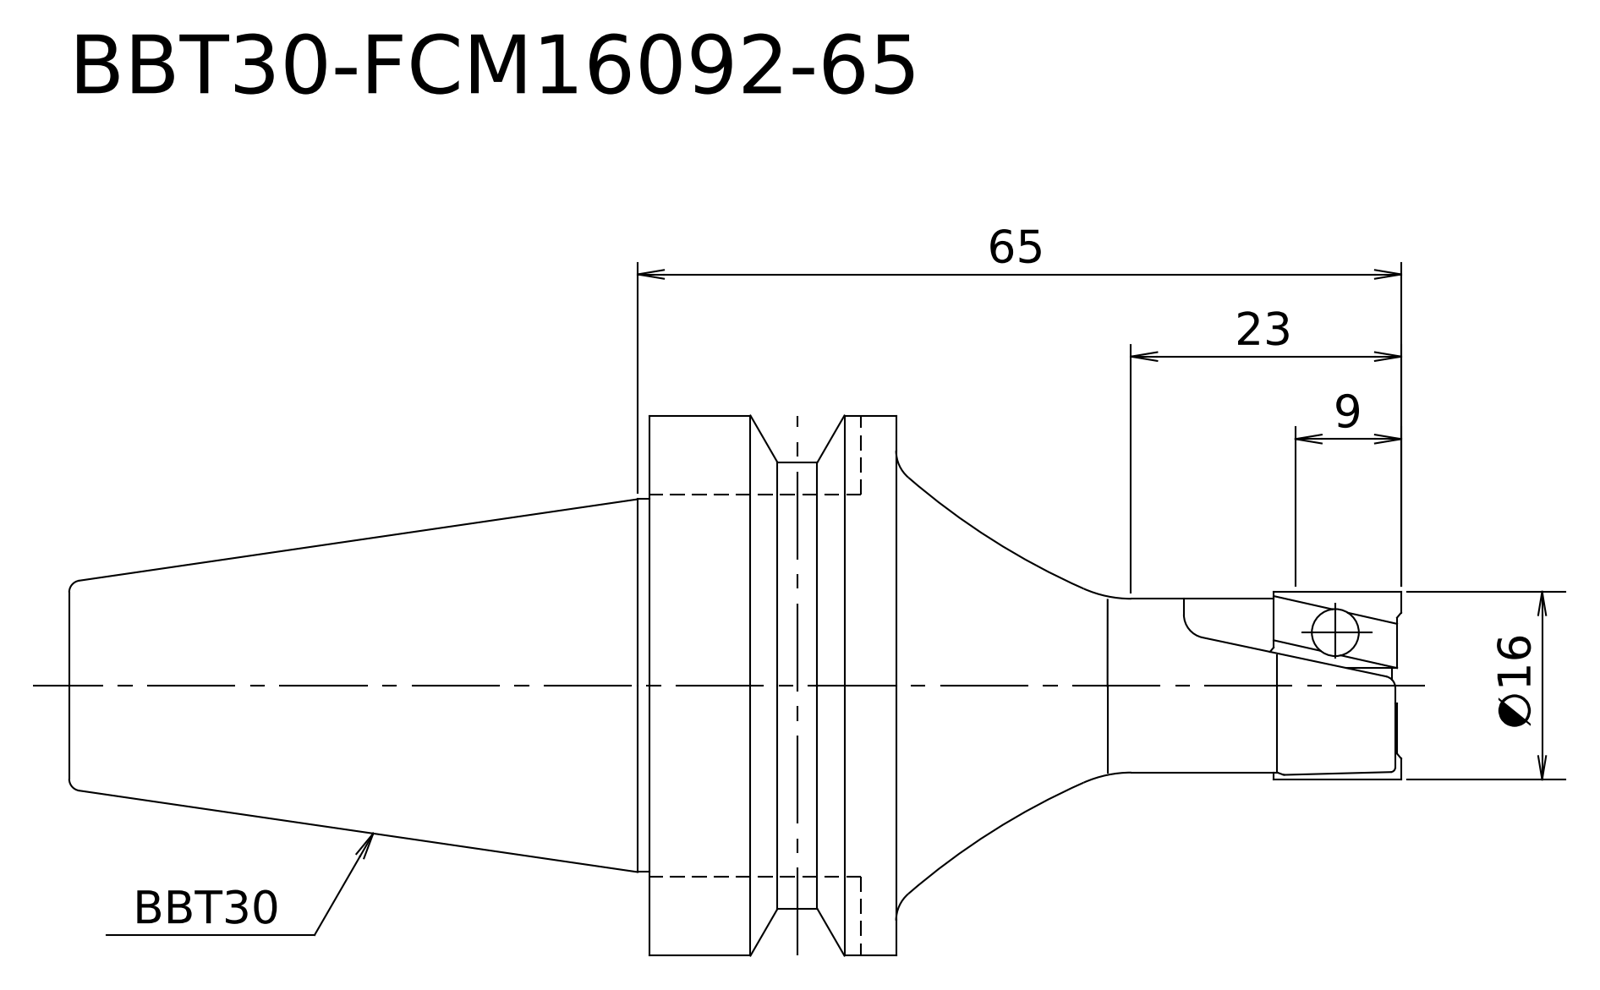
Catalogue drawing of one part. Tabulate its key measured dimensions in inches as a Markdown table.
| quantity | value |
| --- | --- |
| STEP written by | Kubotek KeyCreator V8.5.1 (14335) (CONFIG_CONTROL_DESIGN) |
| units | inches |
| bodies | 1 solid, 17 faces (4 planar, 6 cylindrical, 7 other) |
| overall size | 4.465 × 1.811 × 1.811 |
| volume | 4.331 in³ |
| surface area | 18.87 in² |
| round bosses / shafts (diameter × count) | 1.811 × 1, 1.496 × 1, 1.25 × 1, 0.632 × 1, 0.585 × 1 |
| main face-to-face distances | 0.827, 2.772, 1.945, 1.693, 2.52, 4.465 |
